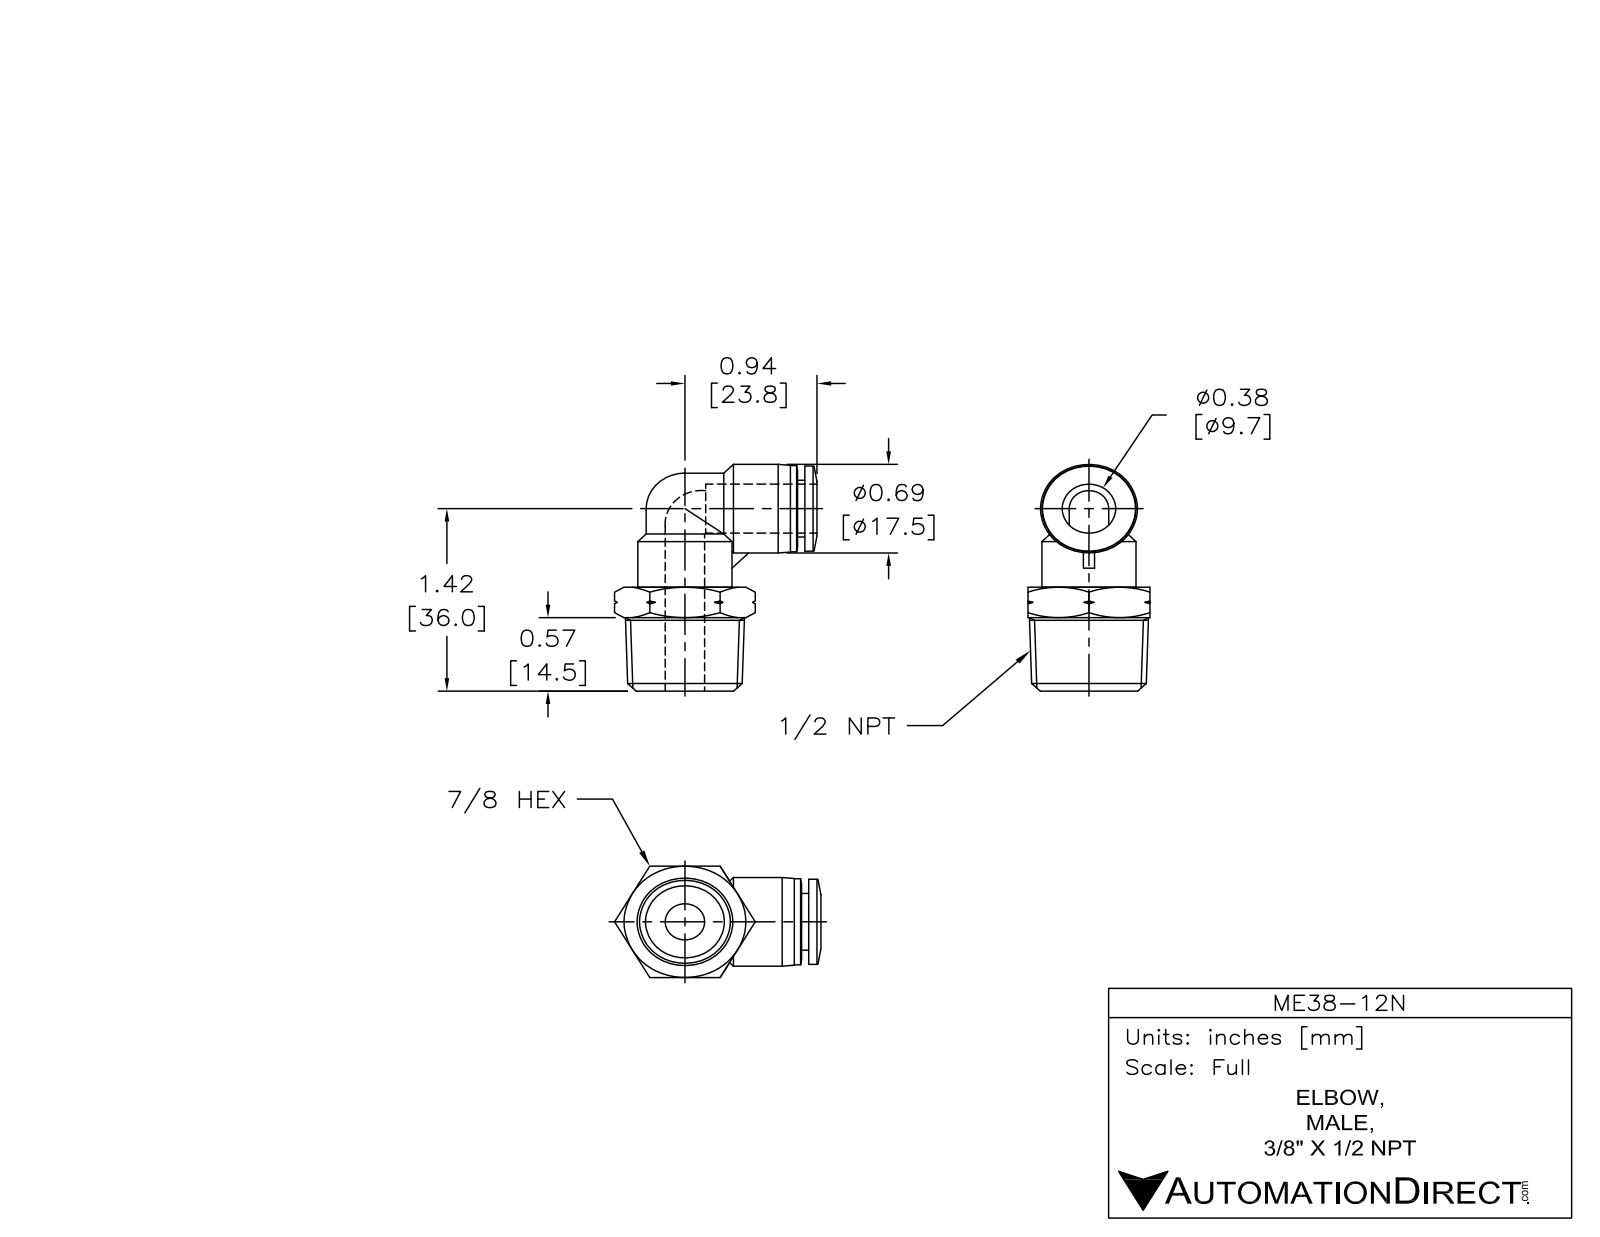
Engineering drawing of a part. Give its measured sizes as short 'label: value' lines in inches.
name: ME38-12N
written by: SolidWorks 2015 (AUTOMOTIVE_DESIGN)
unit: in
bodies: 1 solid, 87 faces (16 planar, 20 cylindrical, 51 other)
size: 1.762 × 1.467 × 0.866
volume: 0.752 in³; area: 8.92 in²
holes: 2× ⌀0.276, 1× ⌀0.386
bosses: 2× ⌀0.669, 1× ⌀0.689, 1× ⌀0.661, 1× ⌀0.551, 1× ⌀0.441
rounds: 1× R0.276
face distances: 0.866, 0.807, 0.051, 0.654, 0.705, 0.571, 0.236, 0.394, 0.472, 0.079
